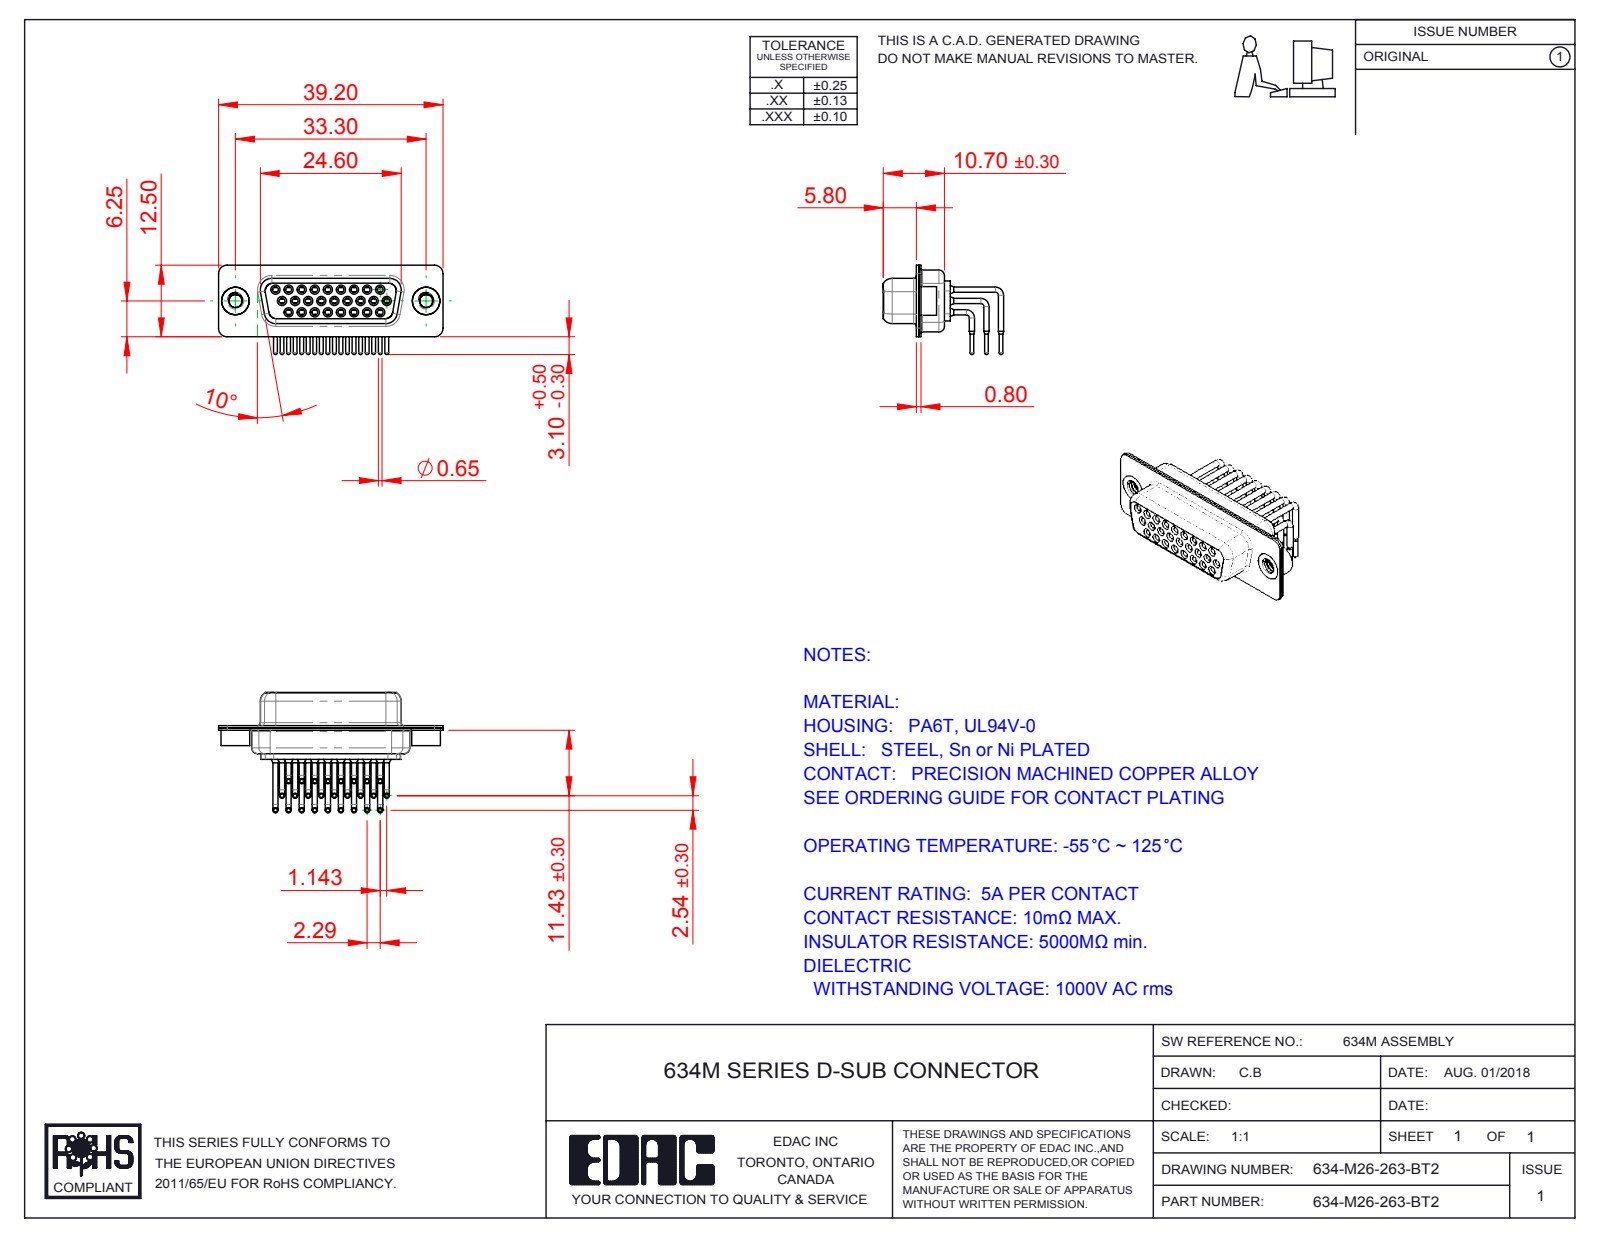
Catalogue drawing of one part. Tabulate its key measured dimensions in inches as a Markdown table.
| quantity | value |
| --- | --- |
| part name | 634M Shell Rear_26 Contacts; 634M Housing_26 Contacts; 634M Contact Row 1; 634M Shell Front_26 Contacts (+4 more) |
| STEP written by | SolidWorks 2016 (CONFIG_CONTROL_DESIGN) |
| units | inches |
| bodies | 31 solids, 1657 faces (457 planar, 735 cylindrical, 465 other) |
| overall size | 1.543 × 0.828 × 0.614 |
| volume | 0.155 in³ |
| surface area | 13.13 in² |
| round holes (diameter × count) | 0.039 × 26, 0.043 × 26, 0.067 × 26, 0.071 × 26, 0.079 × 26, 0.089 × 2, 0.157 × 2, 0.189 × 2 |
| round bosses / shafts (diameter × count) | 0.035 × 52, 0.063 × 26, 0.059 × 26, 0.026 × 26, 0.197 × 2, 0.193 × 2, 0.079 × 1 |
| partial cylindrical surfaces (radius × count) | 0.059 × 16, 0.079 × 12, 0.053 × 8, 0.063 × 8, 0.01 × 4, 0.02 × 4, 0.024 × 4, 0.026 × 4 |
| main face-to-face distances | 0.016, 0.091, 0.057, 0.352, 0.335, 0.075, 0.031, 0.244, 0.018, 0.278 |
| hole center spacings | 0.156, 0.09, 0.18, 0.238, 0.09, 0.324, 0.27, 0.238 |
